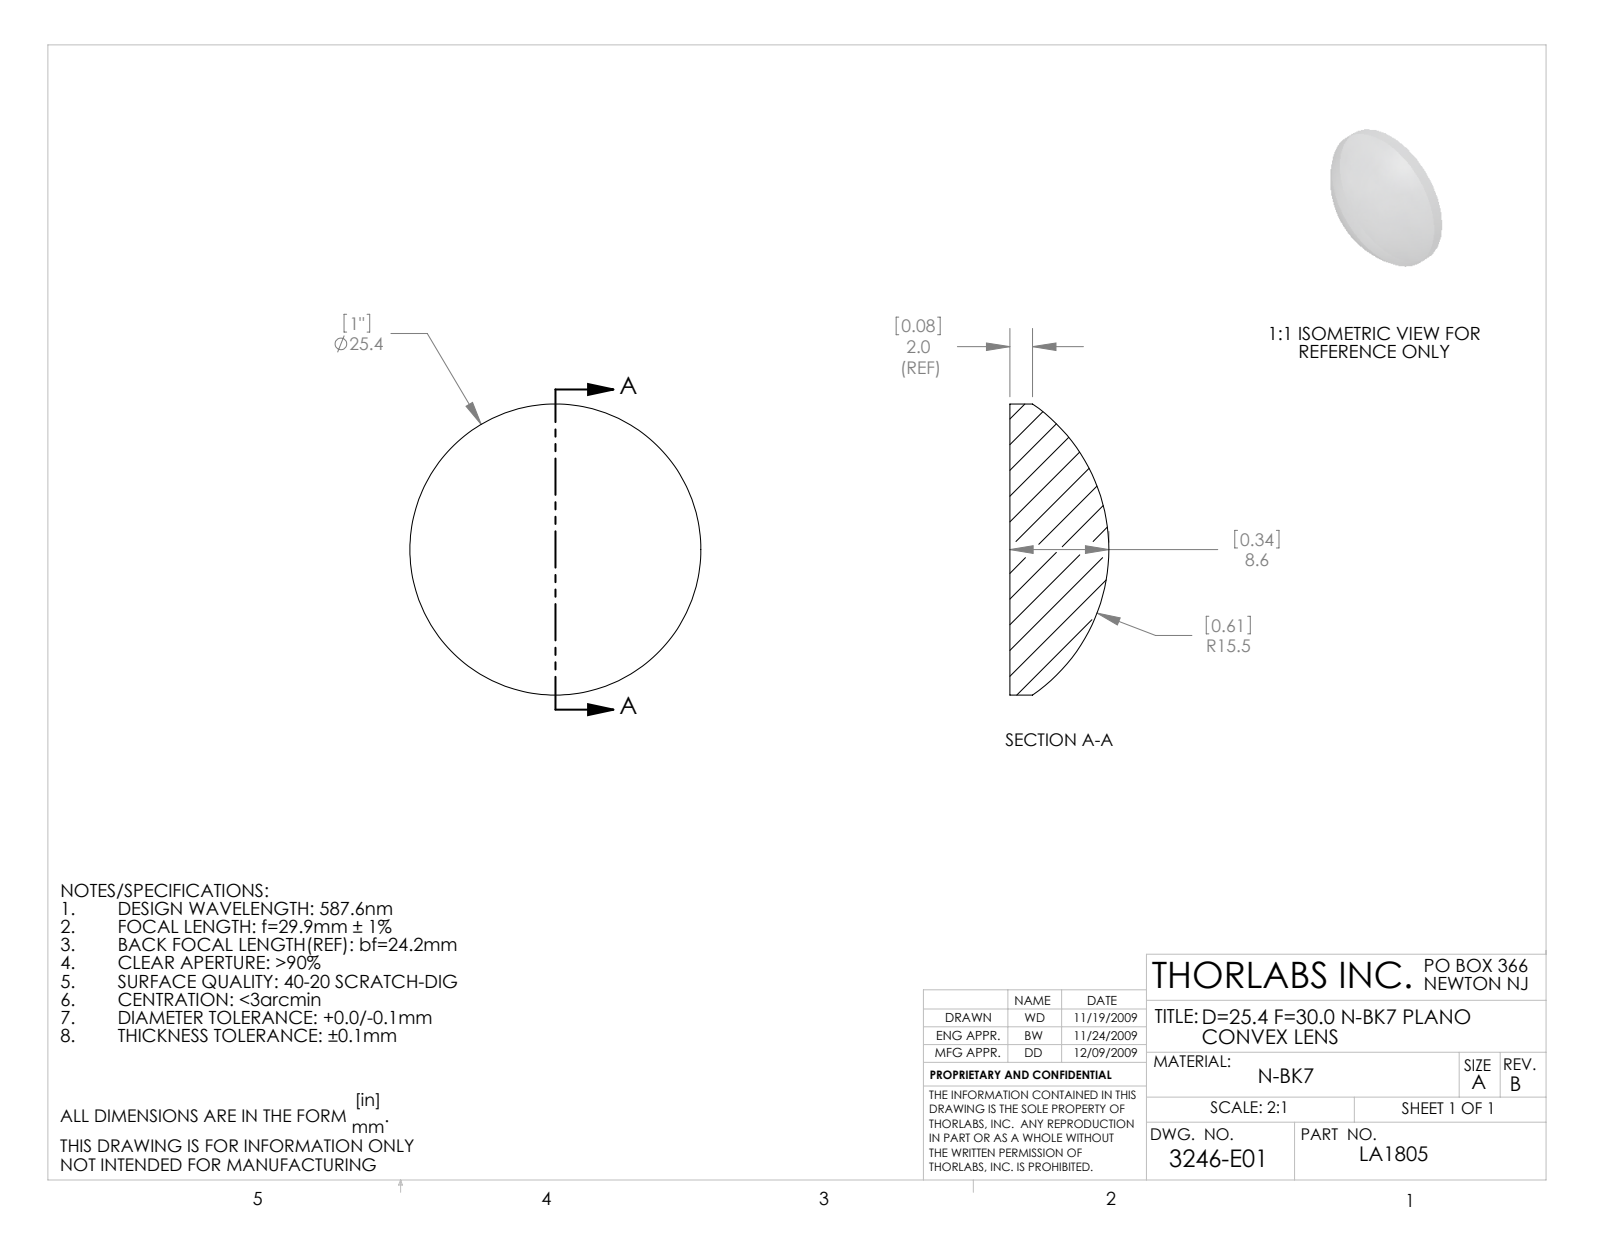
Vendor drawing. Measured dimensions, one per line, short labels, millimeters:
name: 3246-E0W
written by: SolidWorks 2009 (AUTOMOTIVE_DESIGN)
unit: mm
bodies: 1 solid, 5 faces (1 planar, 2 cylindrical, 2 other)
size: 25.4 × 25.4 × 8.64
volume: 2 847 mm³; area: 1 311 mm²
bosses: 1× ⌀25.4
